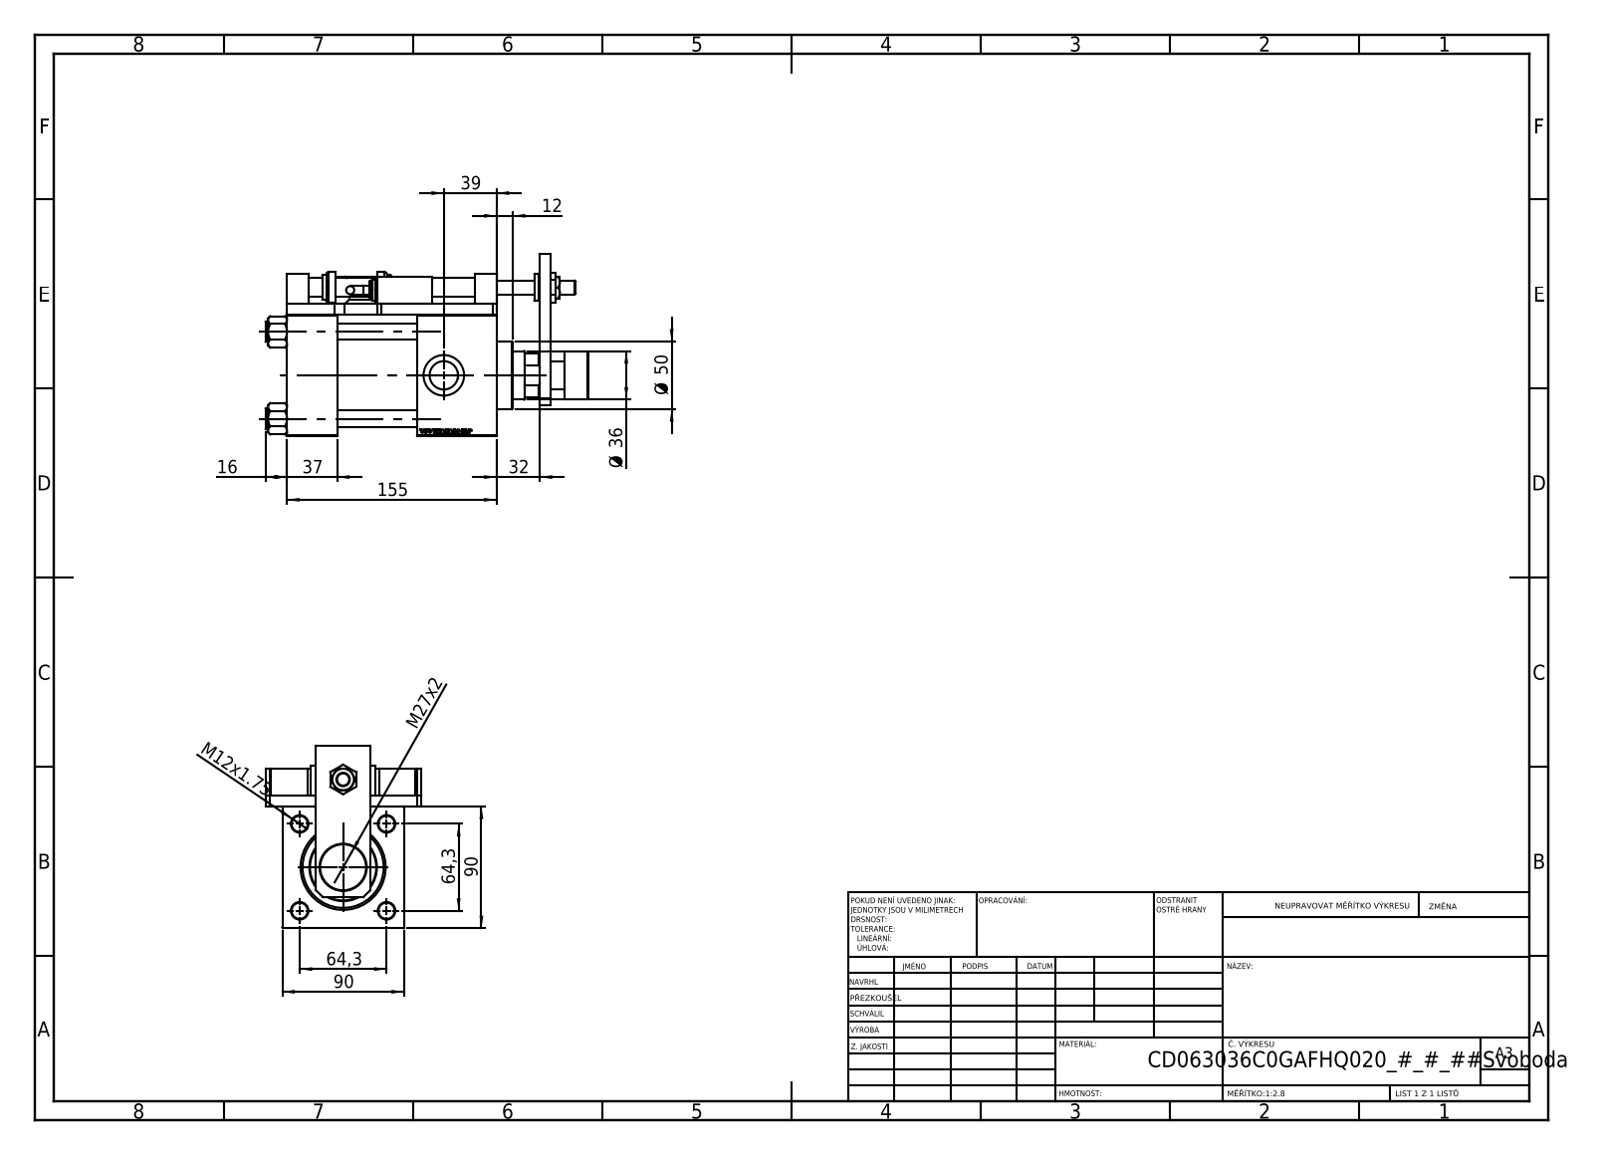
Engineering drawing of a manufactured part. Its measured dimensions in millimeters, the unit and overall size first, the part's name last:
Units: millimetres
Overall size (bounding box): 239 × 135 × 115
Round holes (diameter × count): ⌀8.5 ×4, ⌀12 ×4, ⌀13.5 ×4, ⌀7 ×2, ⌀20.96 ×2, ⌀30 ×2, ⌀10 ×1, ⌀14 ×1, ⌀25.5 ×1, ⌀27 ×1, ⌀36 ×1, ⌀39 ×1
Round bosses / shafts (diameter × count): ⌀15 ×4, ⌀20 ×3, ⌀16 ×2, ⌀14 ×2, ⌀6 ×2, ⌀69 ×1, ⌀35 ×1, ⌀23 ×1
Partial cylindrical surfaces — rounded edges, fillets, slot ends (radius × count): R7.5 ×4
Main face-to-face distances: 8, 90, 37, 59, 118, 98, 155, 20, 32, 91
Hole centre spacings: 45.47, 64.3, 19.14, 32, 45.96, 90.93, 102.33, 129.49
Volume: 1 255 000 mm³ · Surface area: 274 705 mm²
Bodies: 25 solids, 1391 faces (651 planar, 159 cylindrical, 581 other)
Part name (STEP PRODUCT): V215CD_SWITCH_Q_MAGNET; V215CD_SWITCH_Q_PODLOZKA_BACK; V215CD_Body_C; V215CD_SWITCH_Q_SWITCH (+7 more)
STEP written by: SolidWorks 2019 (CONFIG_CONTROL_DESIGN)
